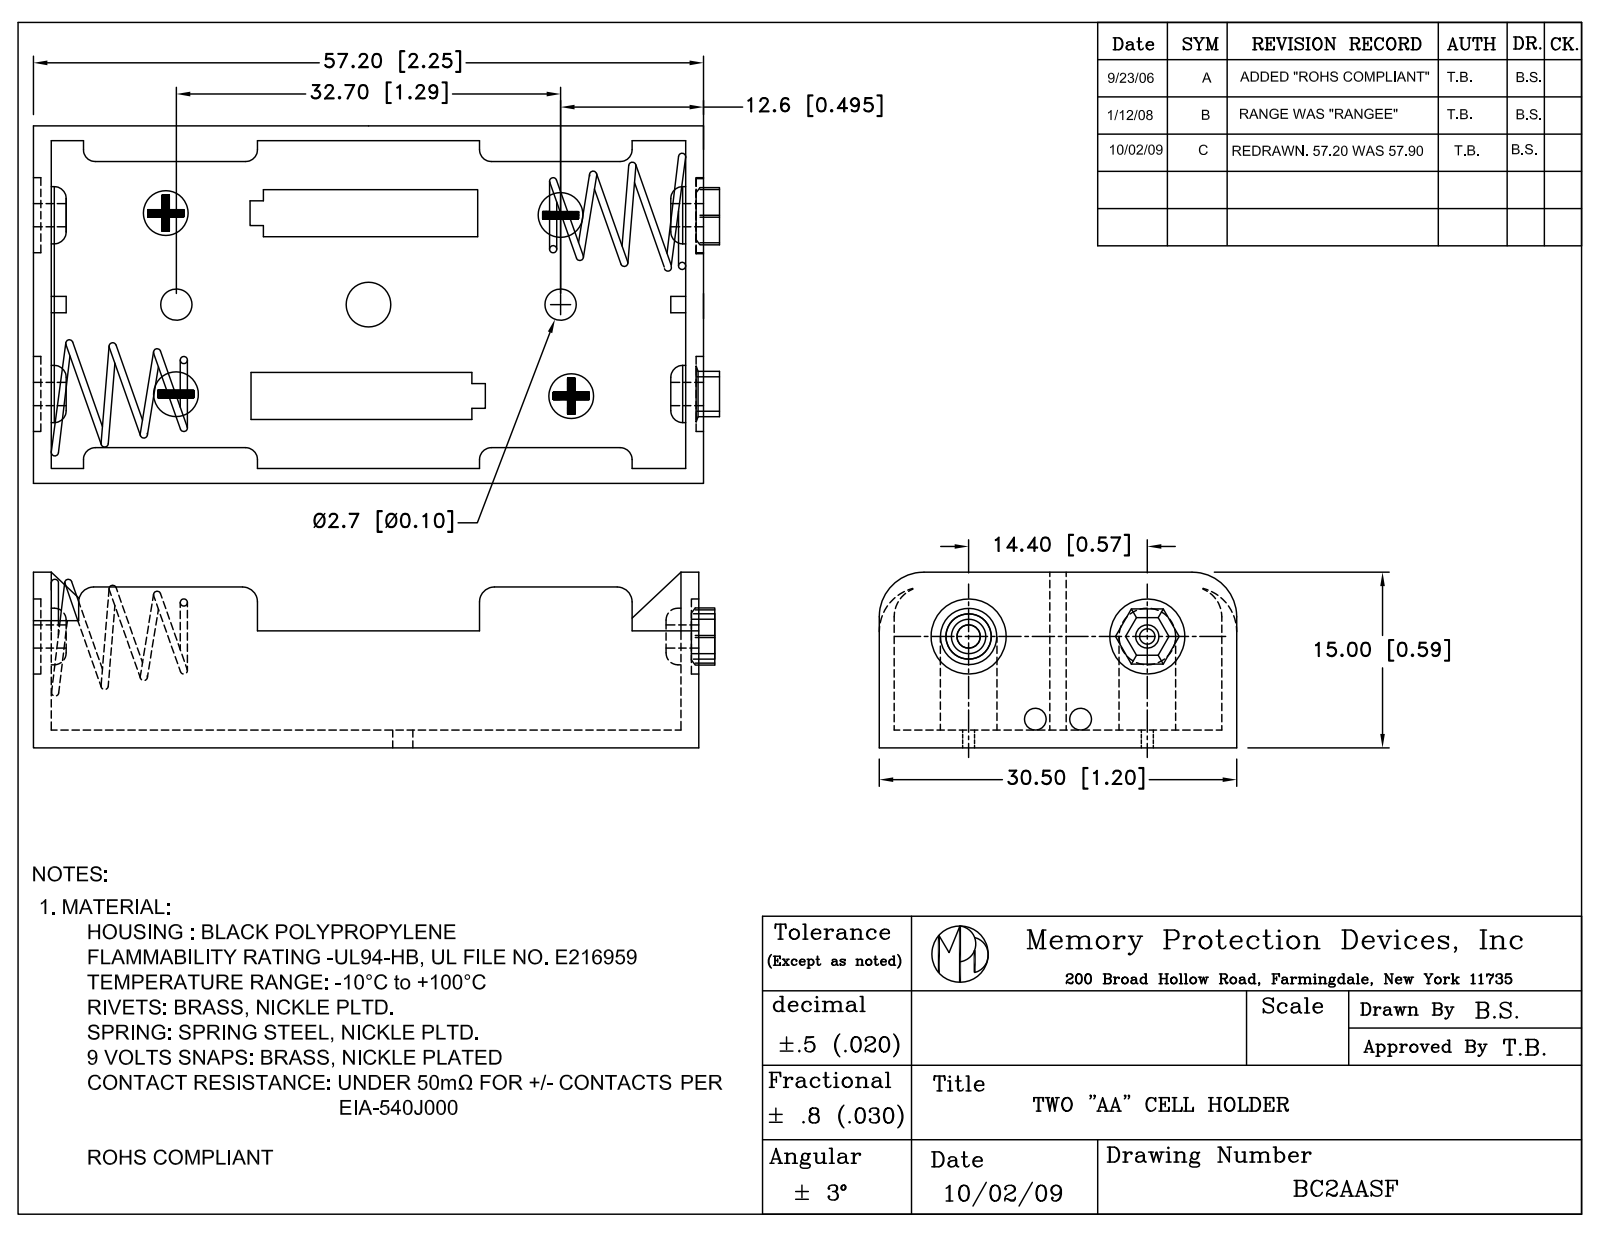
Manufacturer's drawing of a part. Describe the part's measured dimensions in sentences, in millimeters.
The part is named "BC2AASF". Its 3-D file was written by "SolidWorks 2021 (AUTOMOTIVE_DESIGN)". It is 6 solids with 391 faces: 200 planar, 141 cylindrical and 50 other. Overall it measures 61.9 by 30.5 by 15 millimeters. Its volume is 4 542 cubic millimeters and its surface area 8 812 square millimeters. Round holes: 4 of diameter 3.7, 3 of diameter 1.92, 2 of diameter 2, 2 of diameter 2.2, 2 of diameter 2.3, 2 of diameter 2.7, 2 of diameter 3, 2 of diameter 7.6, 2 of diameter 9, 1 of diameter 3.65, 1 of diameter 4.95. Round bosses or shafts: 4 of diameter 4.7, 2 of diameter 6.2, 2 of diameter 3.5, 2 of diameter 0.6, 1 of diameter 7.92, 1 of diameter 5.71, 1 of diameter 0.7. Partial cylindrical surfaces (rounded edges, fillets, slot ends): 12 of radius 0.3, 8 of radius 2.5, 6 of radius 1.02, 2 of radius 2.72, 2 of radius 2.95, 2 of radius 4. The main face-to-face distances are 1.1, 1.55, 29.4, 56.9, 55.8, 28.3, 30.5, 58, 0.31, 57.69. The hole center spacings are 20.47, 8.02, 10.19, 15.25, 36.21, 38, 40.95, 3.1.
